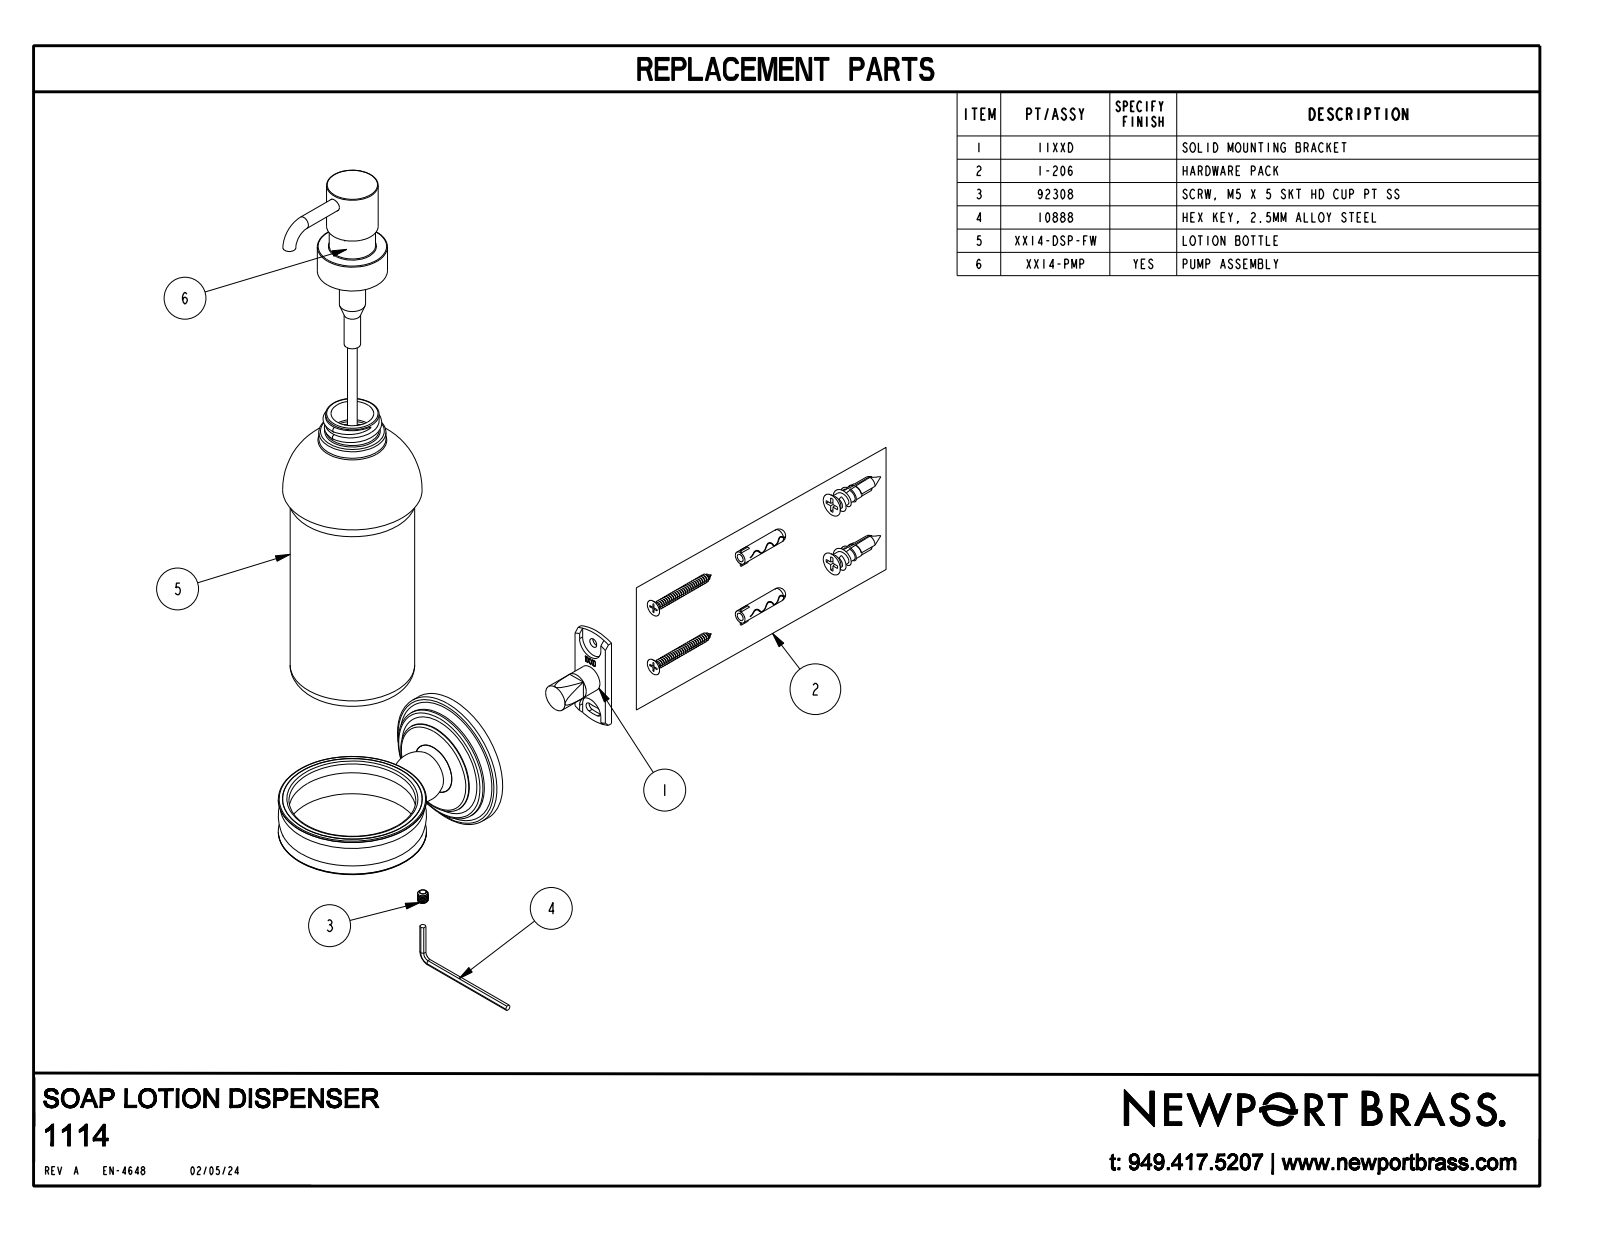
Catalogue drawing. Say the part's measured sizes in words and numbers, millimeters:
The part is named "1114". Its 3-D file was written by "CREO PARAMETRIC BY PTC INC, 2018400 (AUTOMOTIVE_DESIGN)". It is 1 solid with 77 faces: 10 planar, 26 cylindrical and 41 other. Overall it measures 187 by 110.9 by 69 millimeters. Its volume is 436 100 cubic millimeters and its surface area 44 680 square millimeters. Round bosses or shafts: 2 of diameter 24, 1 of diameter 69, 1 of diameter 65, 1 of diameter 58, 1 of diameter 55.4, 1 of diameter 44.4, 1 of diameter 32.6, 1 of diameter 31.2. The main face-to-face distances are 13, 63.7, 19, 44.7, 9.2, 3.8, 4.8, 4.4, 8.2, 75.1.
